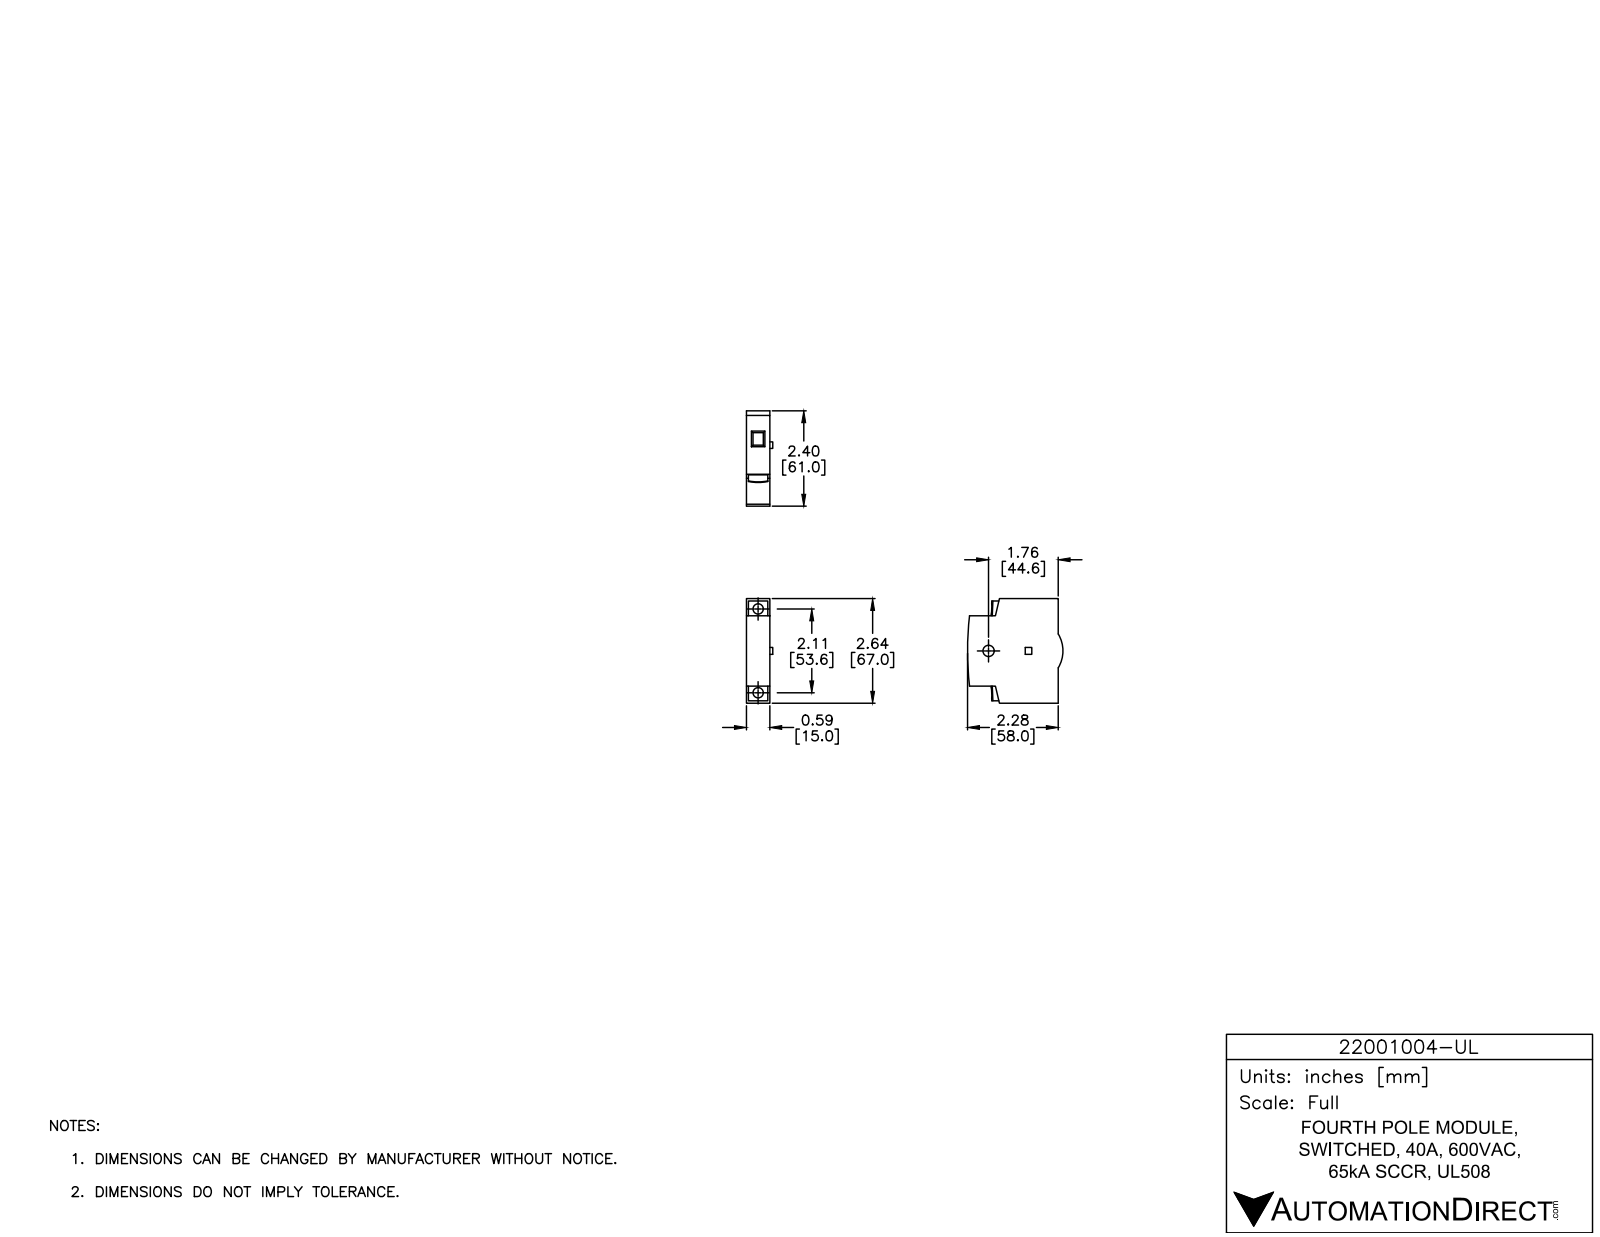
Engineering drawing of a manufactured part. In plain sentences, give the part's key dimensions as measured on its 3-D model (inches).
The part is named "22001004-UL". Its 3-D file was written by "SolidWorks 2015 (AUTOMOTIVE_DESIGN)". It is 1 solid with 61 faces: 46 planar, 11 cylindrical and 4 other. Overall it measures 2.638 by 2.402 by 0.665 inches. Its volume is 3.141 cubic inches and its surface area 18.13 square inches. Round holes: 2 of diameter 0.26, 1 of diameter 0.283. Partial cylindrical surfaces (rounded edges, fillets, slot ends): 1 of radius 0.827, 1 of radius 7.874. The main face-to-face distances are 0.591, 2.638, 0.433, 2.205, 1.772, 0.063, 2.575, 0.37, 2.142, 0.051. The hole center spacings are 2.11.
